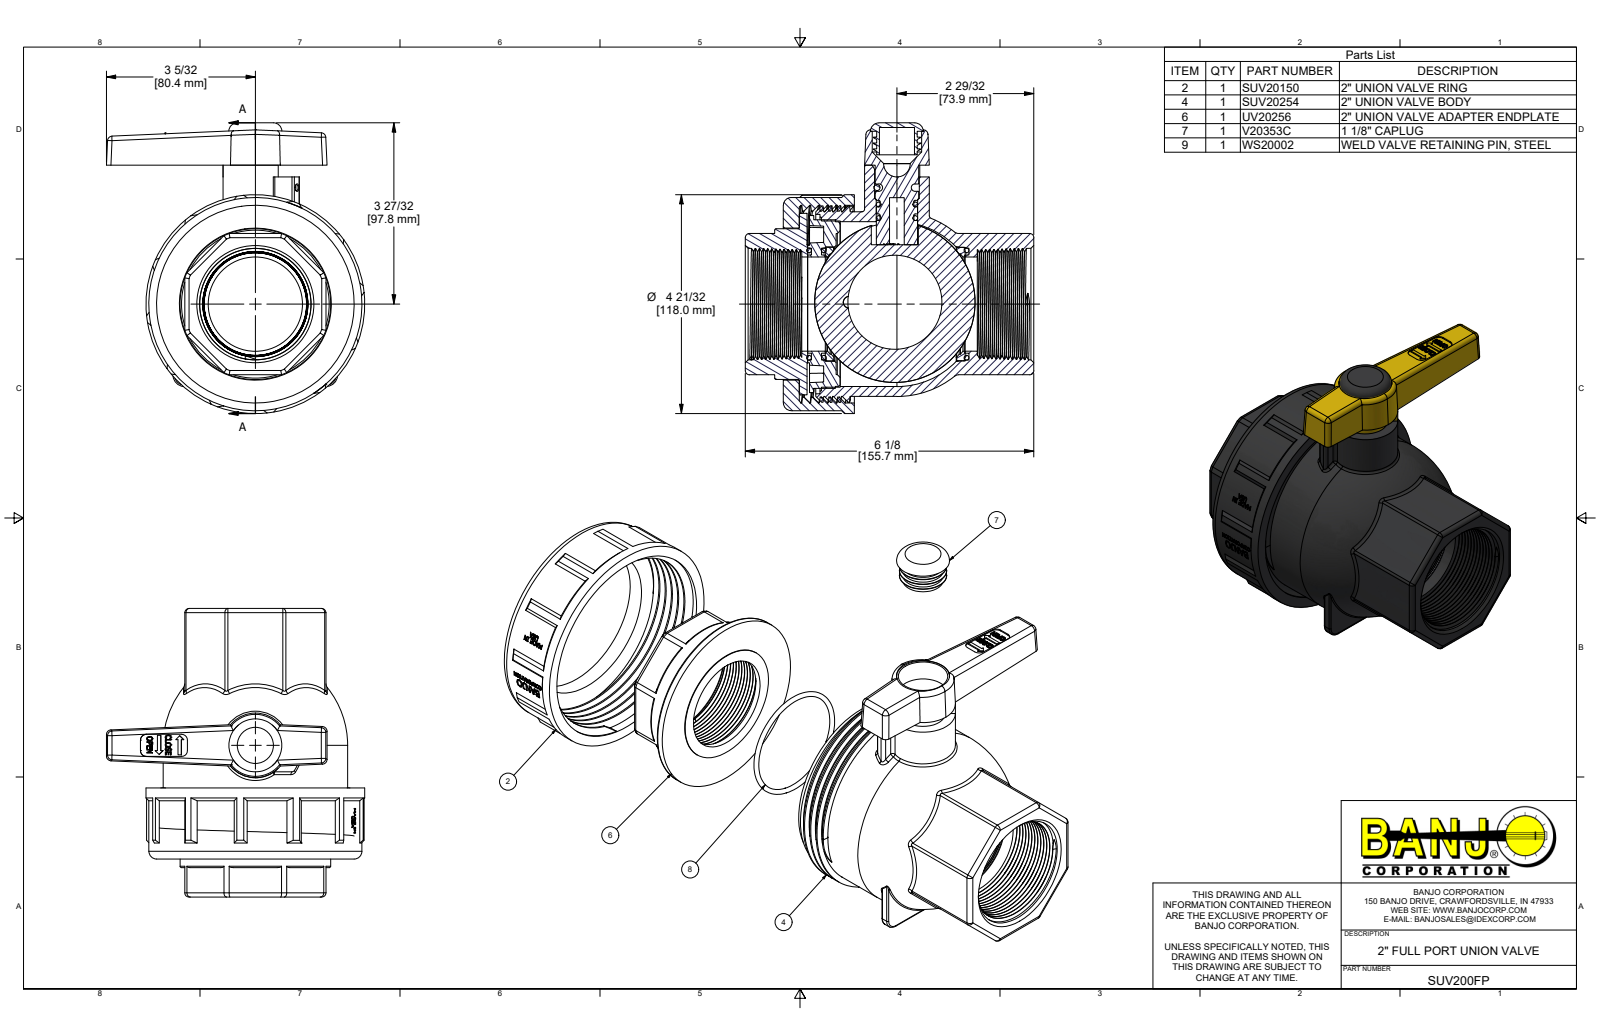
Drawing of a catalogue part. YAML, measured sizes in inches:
part_name: "SUV200FP; SUV20254; SUV20153; SUV20150 (+8 more)"
step_written_by: "Autodesk Inventor 2022 (AUTOMOTIVE_DESIGN)"
units: inches
bodies: {solids: 15, faces: 1346, planar: 564, cylindrical: 236, other: 546}
overall_size: [6.174, 6.13, 5.489]
volume: 42.65
surface_area: 375.3
round_holes:
  - {diameter: 2, count: 2}
  - {diameter: 0.313, count: 1}
  - {diameter: 0.563, count: 1}
  - {diameter: 0.744, count: 1}
  - {diameter: 0.878, count: 1}
  - {diameter: 0.948, count: 1}
  - {diameter: 1.05, count: 1}
  - {diameter: 1.125, count: 1}
  - {diameter: 2.13, count: 1}
  - {diameter: 2.376, count: 1}
  - {diameter: 2.428, count: 1}
  - {diameter: 2.995, count: 1}
round_bosses_or_shafts:
  - {diameter: 4.648, count: 1}
  - {diameter: 4.528, count: 1}
  - {diameter: 4.168, count: 1}
  - {diameter: 3.92, count: 1}
  - {diameter: 3.855, count: 1}
  - {diameter: 3.76, count: 1}
  - {diameter: 3.58, count: 1}
  - {diameter: 3.495, count: 1}
partial_cylinders:
  - {radius: 0.09, count: 24}
  - {radius: 0.1, count: 10}
  - {radius: 0.03, count: 6}
  - {radius: 0.125, count: 5}
  - {radius: 0.06, count: 4}
  - {radius: 1.104, count: 4}
  - {radius: 0.078, count: 2}
  - {radius: 0.25, count: 2}
face_to_face_distances: [0.34, 0.165, 0.505, 2.999, 0.518, 3, 0.08, 0.178, 0.053, 0.218]
